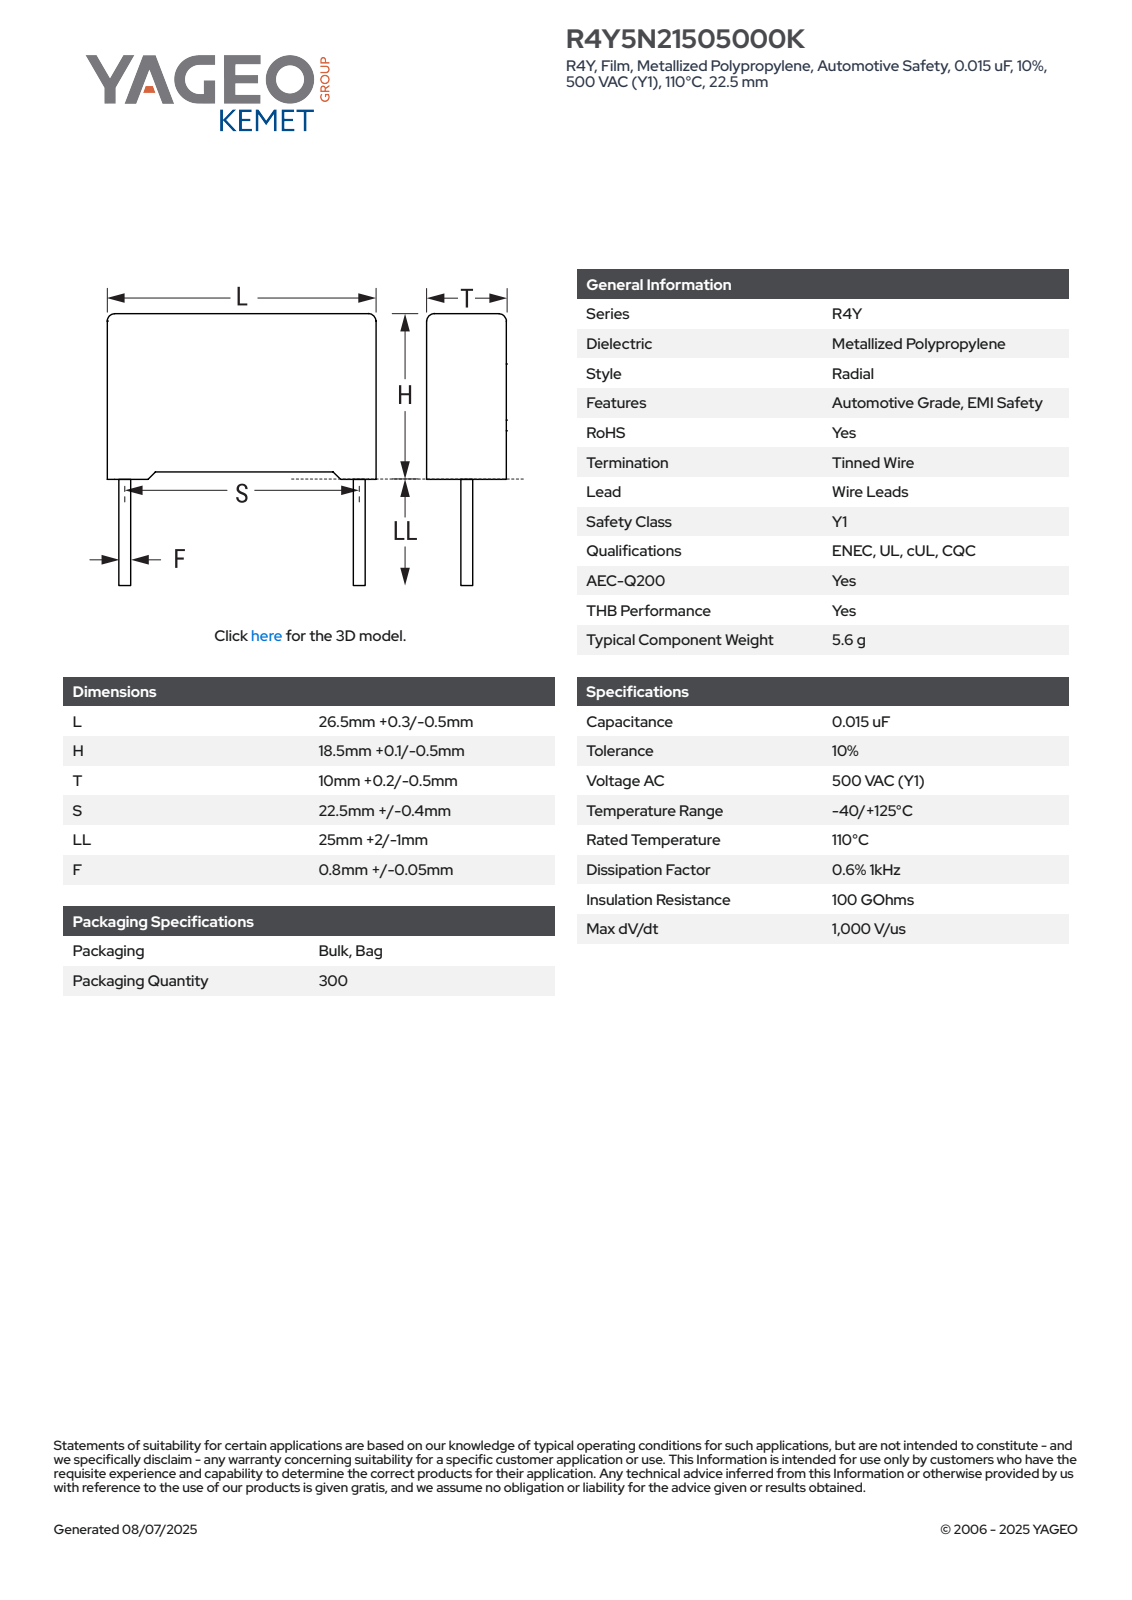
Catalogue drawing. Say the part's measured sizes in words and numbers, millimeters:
The part is named "CFR_RB2_26.5X18.5X1_L26.8H18.6T10.2S22.5LL27F0.85". Its 3-D file was written by "SolidWorks 2021 (AUTOMOTIVE_DESIGN)". It is 4 solids with 85 faces: 77 planar, 8 cylindrical and 0 other. Overall it measures 45.6 by 26.8 by 10.21 millimeters. Its volume is 4 933 cubic millimeters and its surface area 2 112 square millimeters. Round bosses or shafts: 2 of diameter 0.85. Partial cylindrical surfaces (rounded edges, fillets, slot ends): 4 of radius 0.5. The main face-to-face distances are 10.2, 17.85, 26.8, 17.96, 0.75, 0.64, 18.6, 0.89, 9.31, 25.91.
